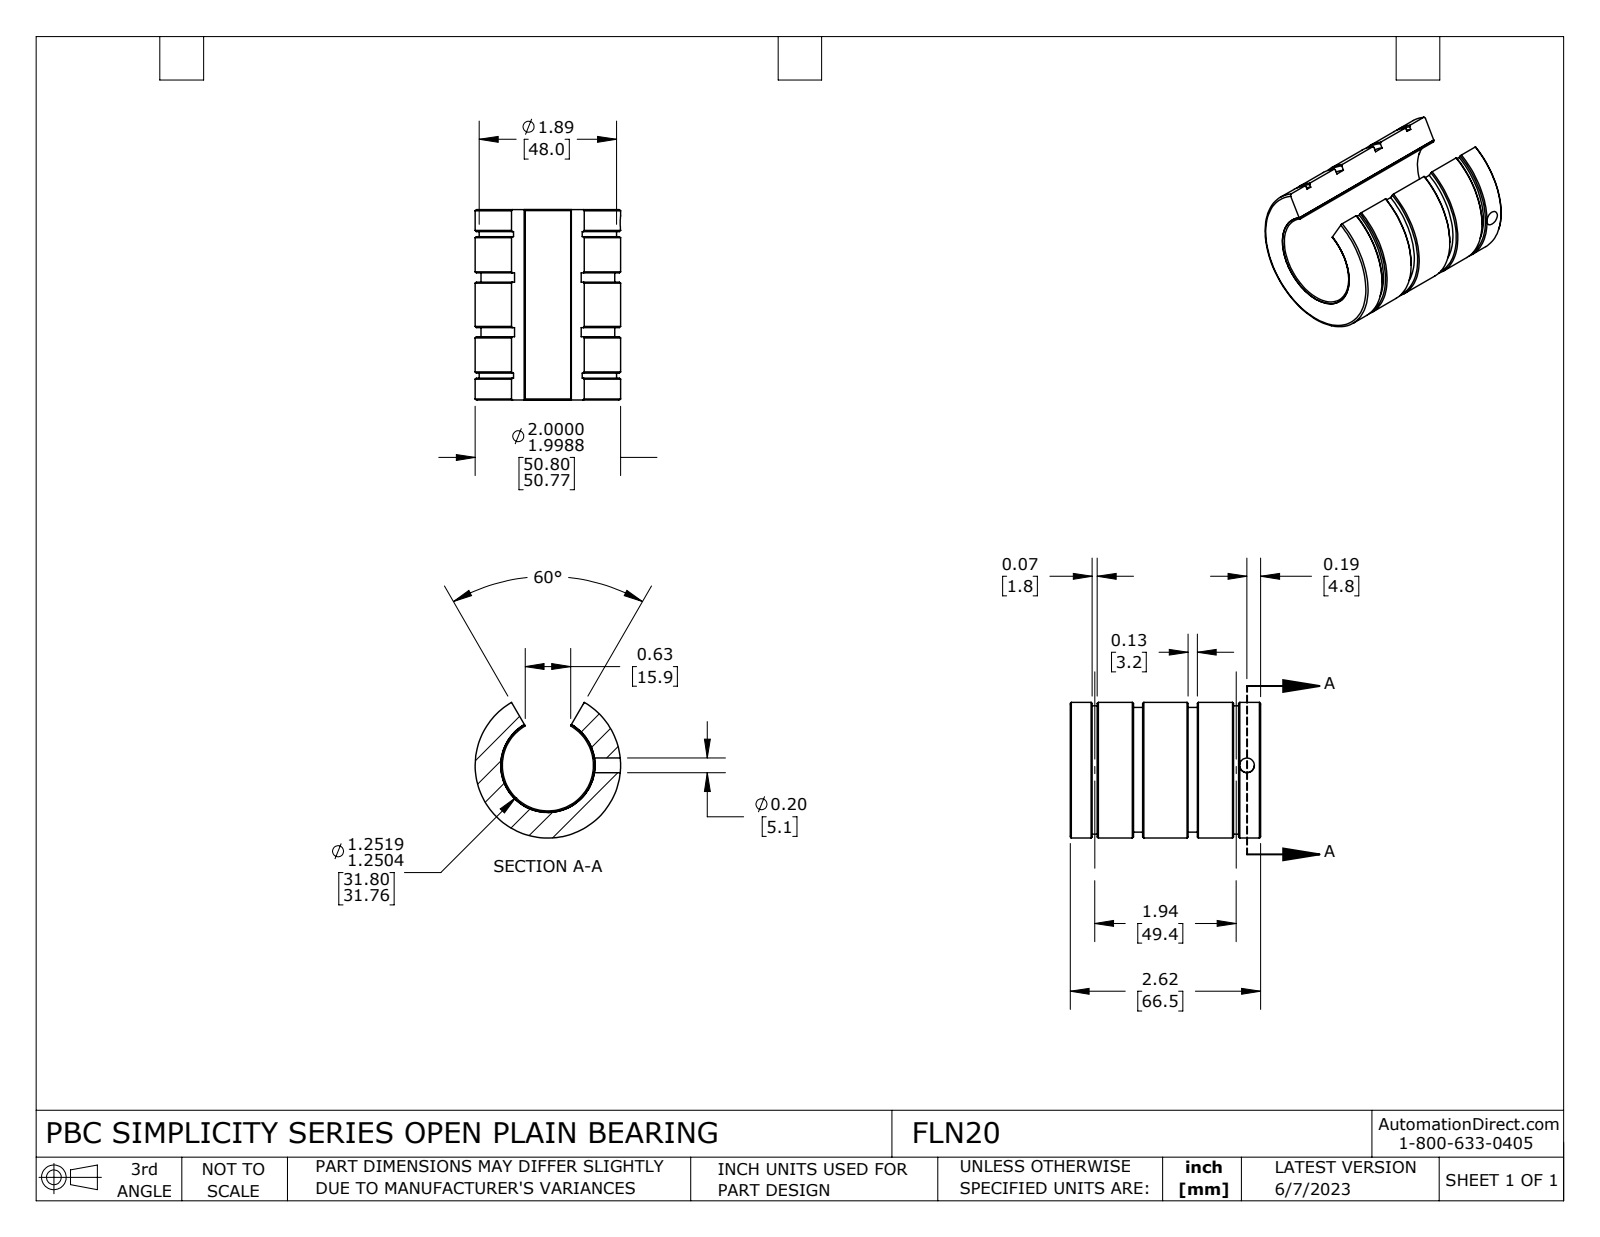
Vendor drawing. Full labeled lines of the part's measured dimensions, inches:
Part name (STEP PRODUCT): FLN20
STEP written by: SolidWorks 2021 (CONFIG_CONTROL_DESIGN)
Units: inches
Bodies: 2 solids, 82 faces (14 planar, 40 cylindrical, 28 other)
Overall size (bounding box): 2.618 × 1.999 × 1.865
Volume: 4.004 in³ · Surface area: 47.26 in²
Round holes (diameter × count): ⌀0.201 ×1, ⌀1.252 ×1, ⌀1.295 ×1
Round bosses / shafts (diameter × count): ⌀1.999 ×1, ⌀1.889 ×1, ⌀1.838 ×1
Main face-to-face distances: 2.617, 0.87, 1.747, 0.996, 1.621, 0.126, 0.751, 0.302, 2.316, 0.569
